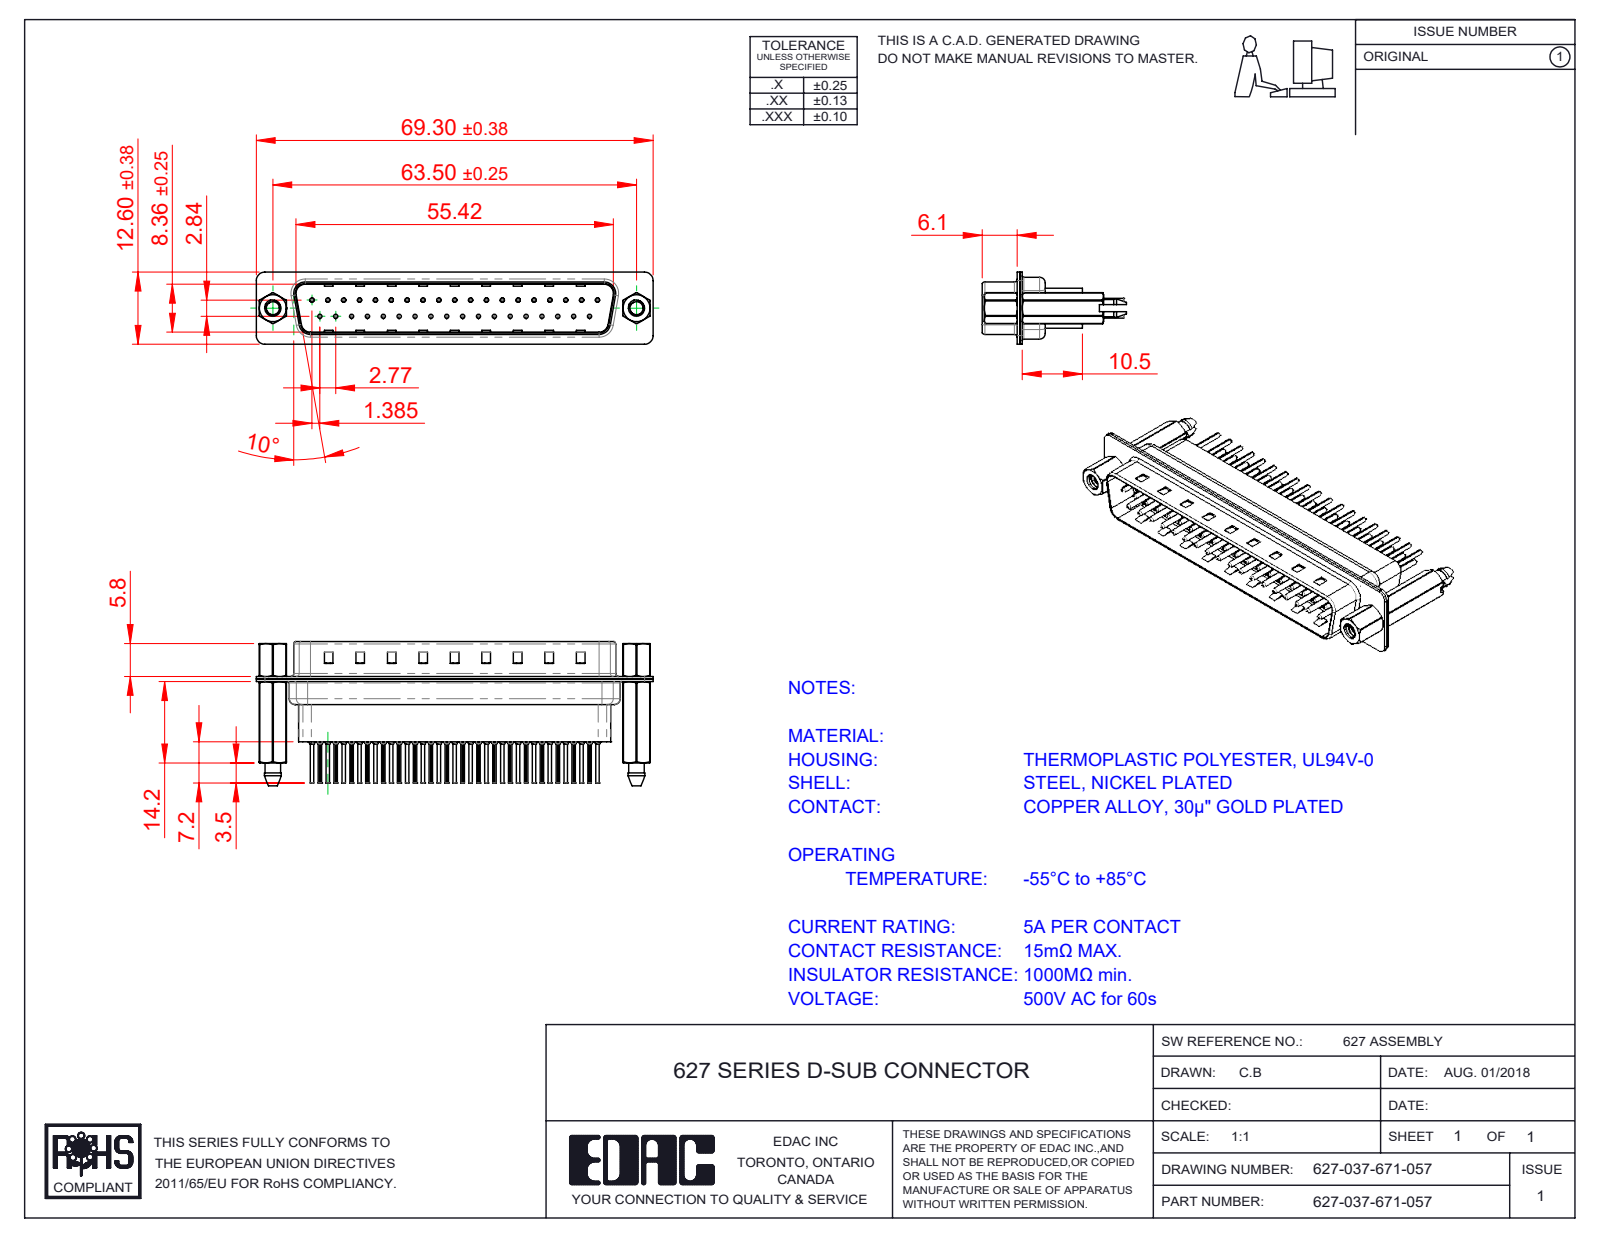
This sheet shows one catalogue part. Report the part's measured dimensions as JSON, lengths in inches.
{"part_name": "627 4-40 Hex Standoff; 627 Contact Row 1_61; 627-037-671-057; 627 Shell Front_37 Contacts (+4 more)", "step_written_by": "SolidWorks 2020 (CONFIG_CONTROL_DESIGN)", "units": "inches", "bodies": {"solids": 44, "faces": 4272, "planar": 1145, "cylindrical": 1648, "other": 1479}, "overall_size": [2.728, 0.988, 0.496], "volume_in3": 0.361, "surface_area_in2": 23.54, "round_holes": [[0.008, 37], [0.014, 37], [0.043, 37], [0.063, 37], [0.089, 2], [0.09, 2], [0.157, 2], [0.189, 2]], "round_bosses_or_shafts": [[0.079, 37], [0.059, 37], [0.03, 37], [0.024, 37], [0.193, 2], [0.11, 2]], "partial_cylinders_radius": [[0.004, 74], [0.059, 18], [0.079, 12], [0.063, 10], [0.02, 8], [0.01, 4], [0.024, 4], [0.026, 4]], "face_to_face_distances": [0.016, 0.032, 0.377, 0.018, 0.027, 0.302, 0.059, 0.043, 0.318, 0.345], "hole_center_spacings": [0.124, 0.109, 0.218, 0.327, 0.198, 0.398, 0.436, 0.503]}
